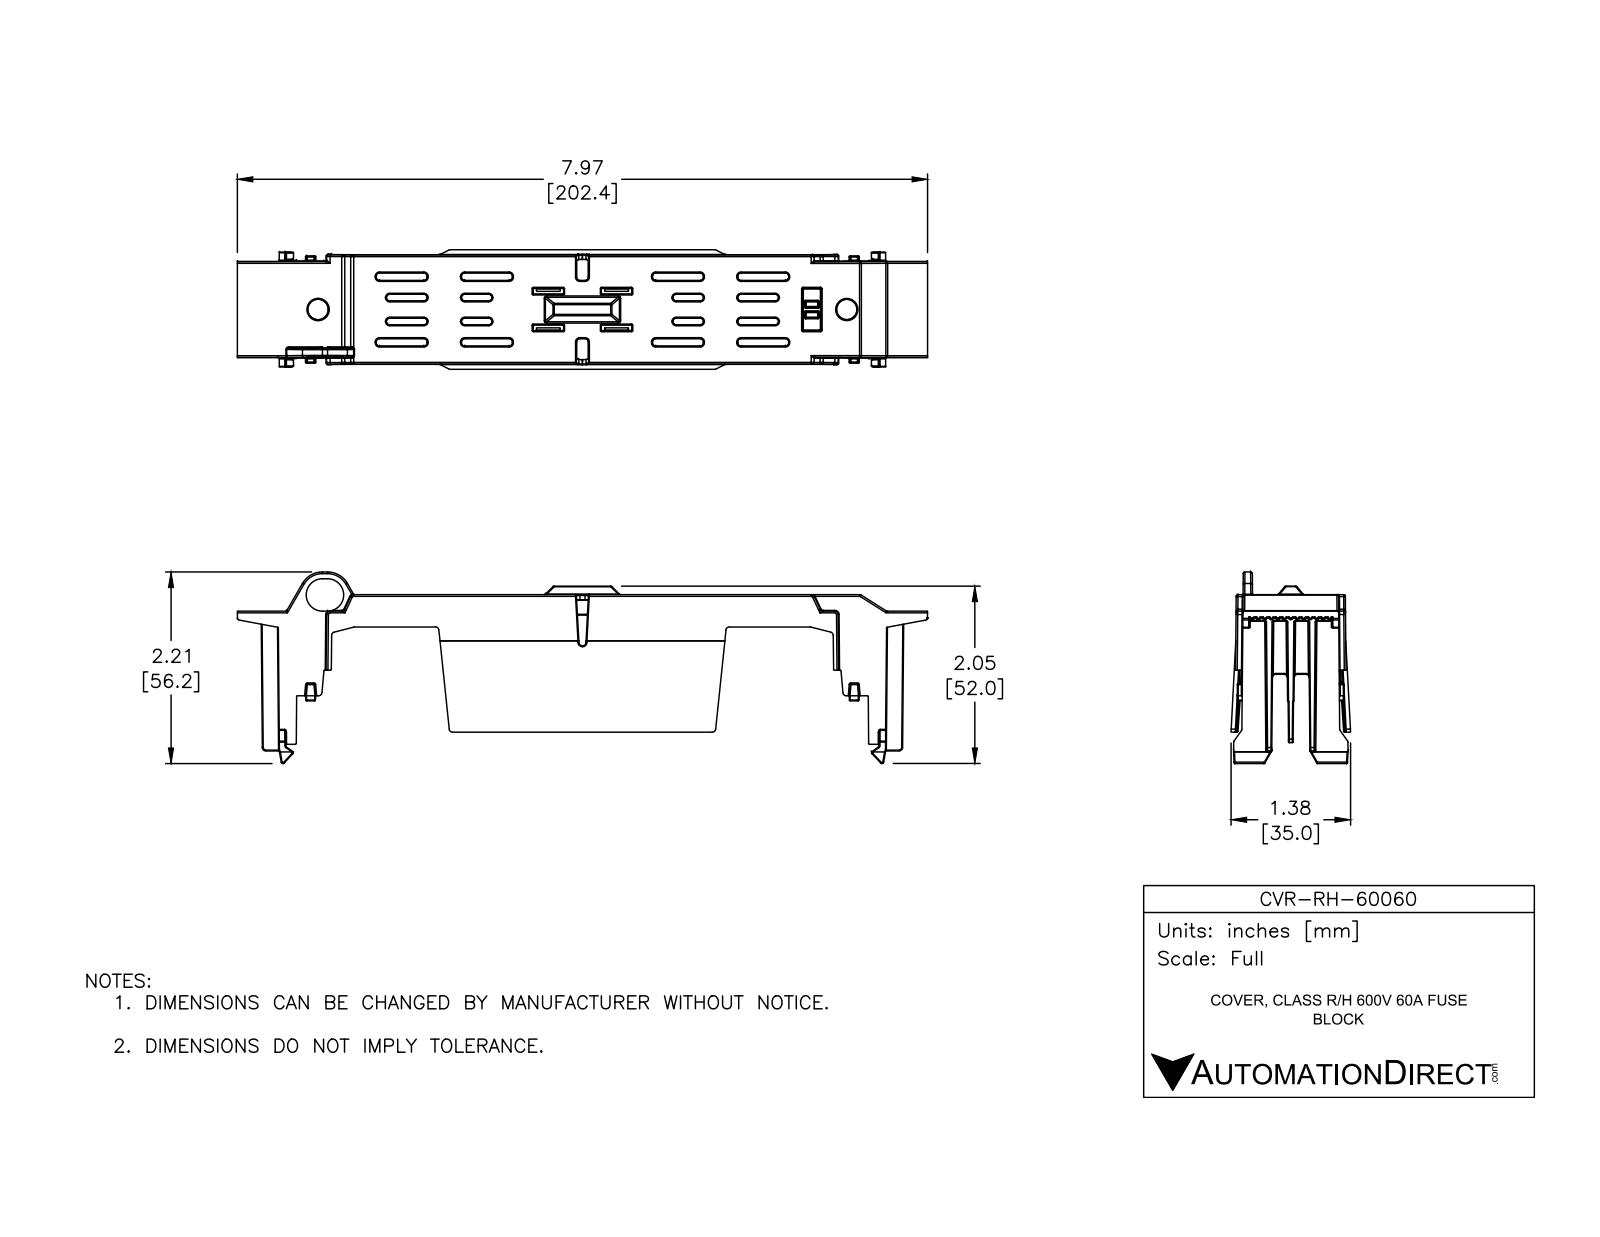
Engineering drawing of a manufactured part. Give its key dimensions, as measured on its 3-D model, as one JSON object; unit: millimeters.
{"part_name": "CVR-RH-60060", "step_written_by": "SolidWorks 2016 (AUTOMOTIVE_DESIGN)", "units": "millimeters", "bodies": {"solids": 1, "faces": 2823, "planar": 515, "cylindrical": 1271, "other": 1037}, "overall_size": [202.4, 56.2, 35.1], "volume_mm3": 30690, "surface_area_mm2": 40550, "partial_cylinders_radius": [[0.3, 402], [0.2, 259], [1, 100], [0.5, 61], [1.2, 20], [0.8, 4], [1.8, 4], [2.5, 4]], "face_to_face_distances": [1.5, 1.5, 2, 0.5, 3.5, 4.9, 176.1, 3.4, 6.2, 7.3]}
